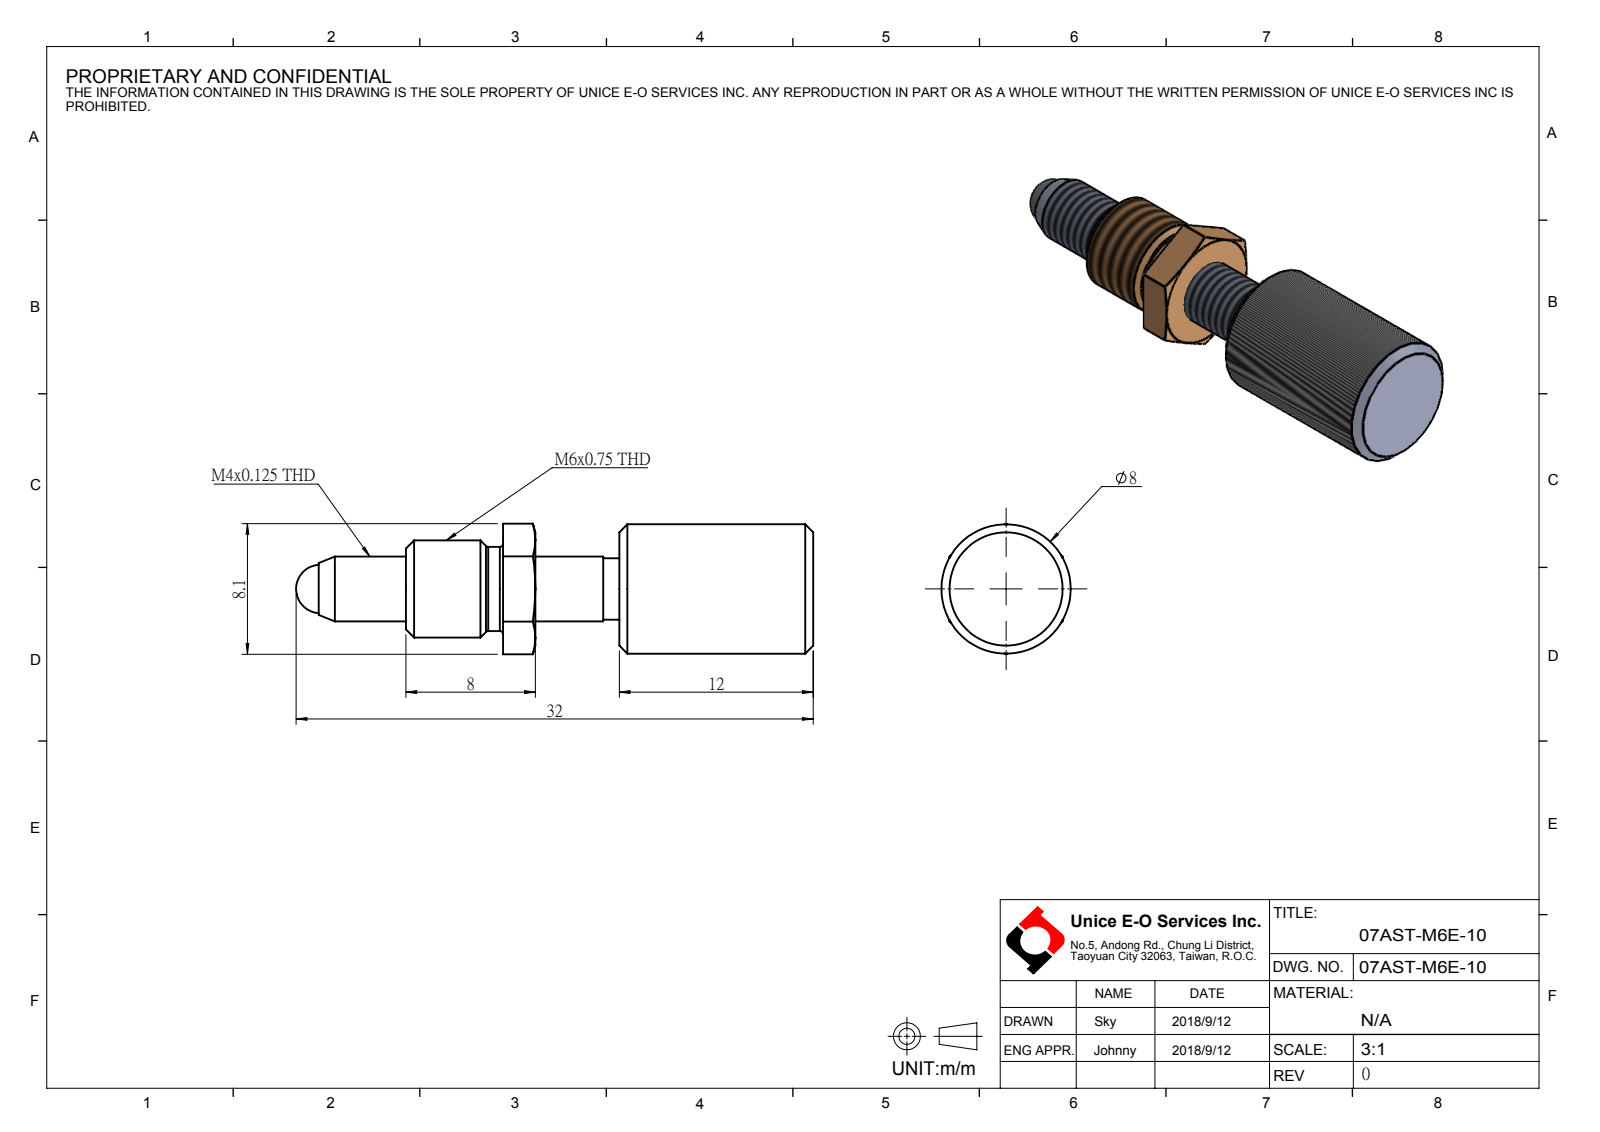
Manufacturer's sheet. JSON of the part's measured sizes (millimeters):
{"part_name": "07AST-M6E-10", "step_written_by": "SolidWorks 2016 (AUTOMOTIVE_DESIGN)", "units": "millimeters", "bodies": {"solids": 0, "faces": 44, "planar": 12, "cylindrical": 10, "other": 22}, "overall_size": [32, 8.08, 8], "round_bosses_or_shafts": [[8, 1], [6, 1], [5.2, 1], [4, 1], [3.8, 1]], "face_to_face_distances": [12, 5.2, 17.2, 7, 2, 7.2, 19.2, 6, 8, 13.2]}
